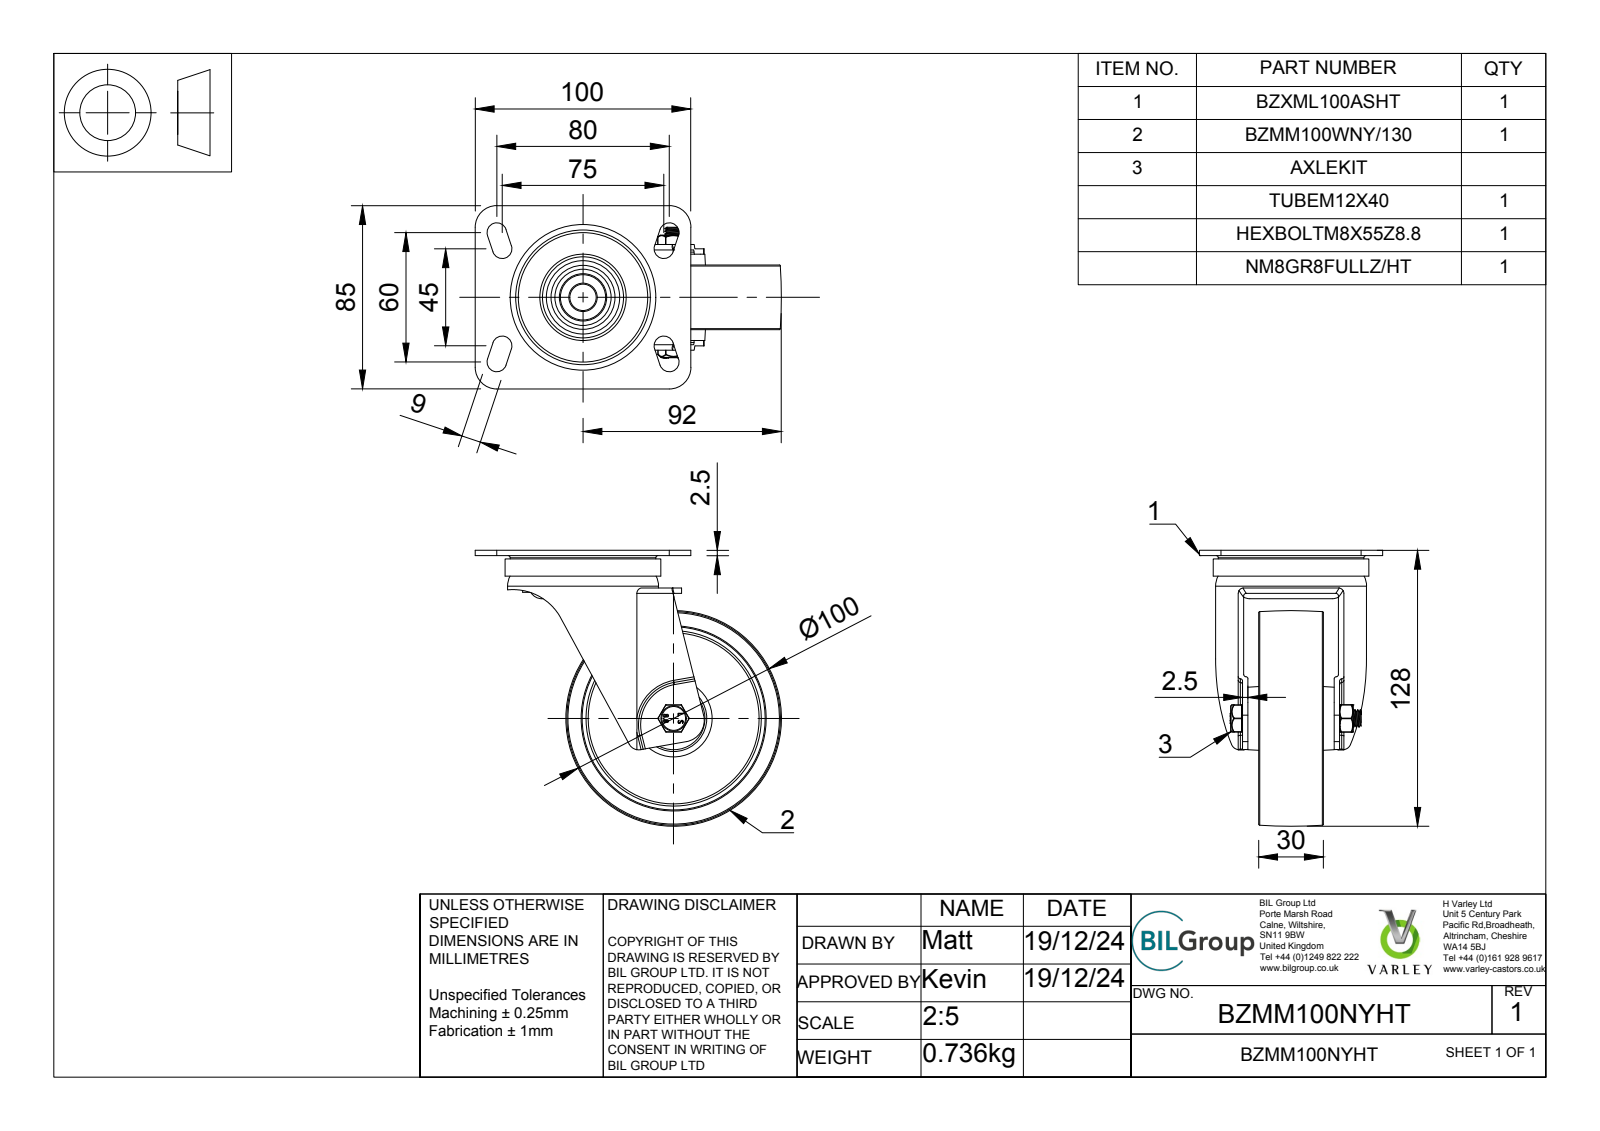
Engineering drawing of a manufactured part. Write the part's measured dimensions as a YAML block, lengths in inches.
part_name: "BZMM100NYHT v3; BZXML100ASHT v1; PRESSED STEEL TOP PLATE; PRESSED STEEL TOP PLATE Geometry (+6 more)"
step_written_by: "Autodesk Translation Framework v13.20.0.188 (AP242_MANAGED_MODEL_BASED_3D_ENGINEERING_MIM_LF)"
units: inches
bodies: {solids: 43, faces: 416, planar: 105, cylindrical: 138, other: 173}
overall_size: [5.591, 5.039, 3.346]
volume: 11.46
surface_area: 157
round_holes:
  - {diameter: 0.026, count: 2}
  - {diameter: 0.315, count: 1}
  - {diameter: 0.319, count: 1}
  - {diameter: 0.331, count: 1}
  - {diameter: 0.48, count: 1}
  - {diameter: 0.492, count: 1}
  - {diameter: 1.496, count: 1}
  - {diameter: 2.559, count: 1}
  - {diameter: 2.766, count: 1}
round_bosses_or_shafts:
  - {diameter: 2.844, count: 1}
  - {diameter: 2.756, count: 1}
  - {diameter: 2.657, count: 1}
  - {diameter: 2.205, count: 1}
  - {diameter: 0.866, count: 1}
  - {diameter: 0.787, count: 1}
  - {diameter: 0.469, count: 1}
  - {diameter: 0.453, count: 1}
partial_cylinders:
  - {radius: 0.01, count: 18}
  - {radius: 0.039, count: 16}
  - {radius: 0.177, count: 8}
  - {radius: 0.394, count: 5}
  - {radius: 0.013, count: 4}
  - {radius: 0.025, count: 4}
  - {radius: 0.049, count: 4}
  - {radius: 0.025, count: 2}
face_to_face_distances: [0.098, 0.118, 0.65, 0.079, 0.531, 0.197, 1.752, 0.177, 0.728, 0.846]
hole_center_spacings: [0.127, 0.098]
